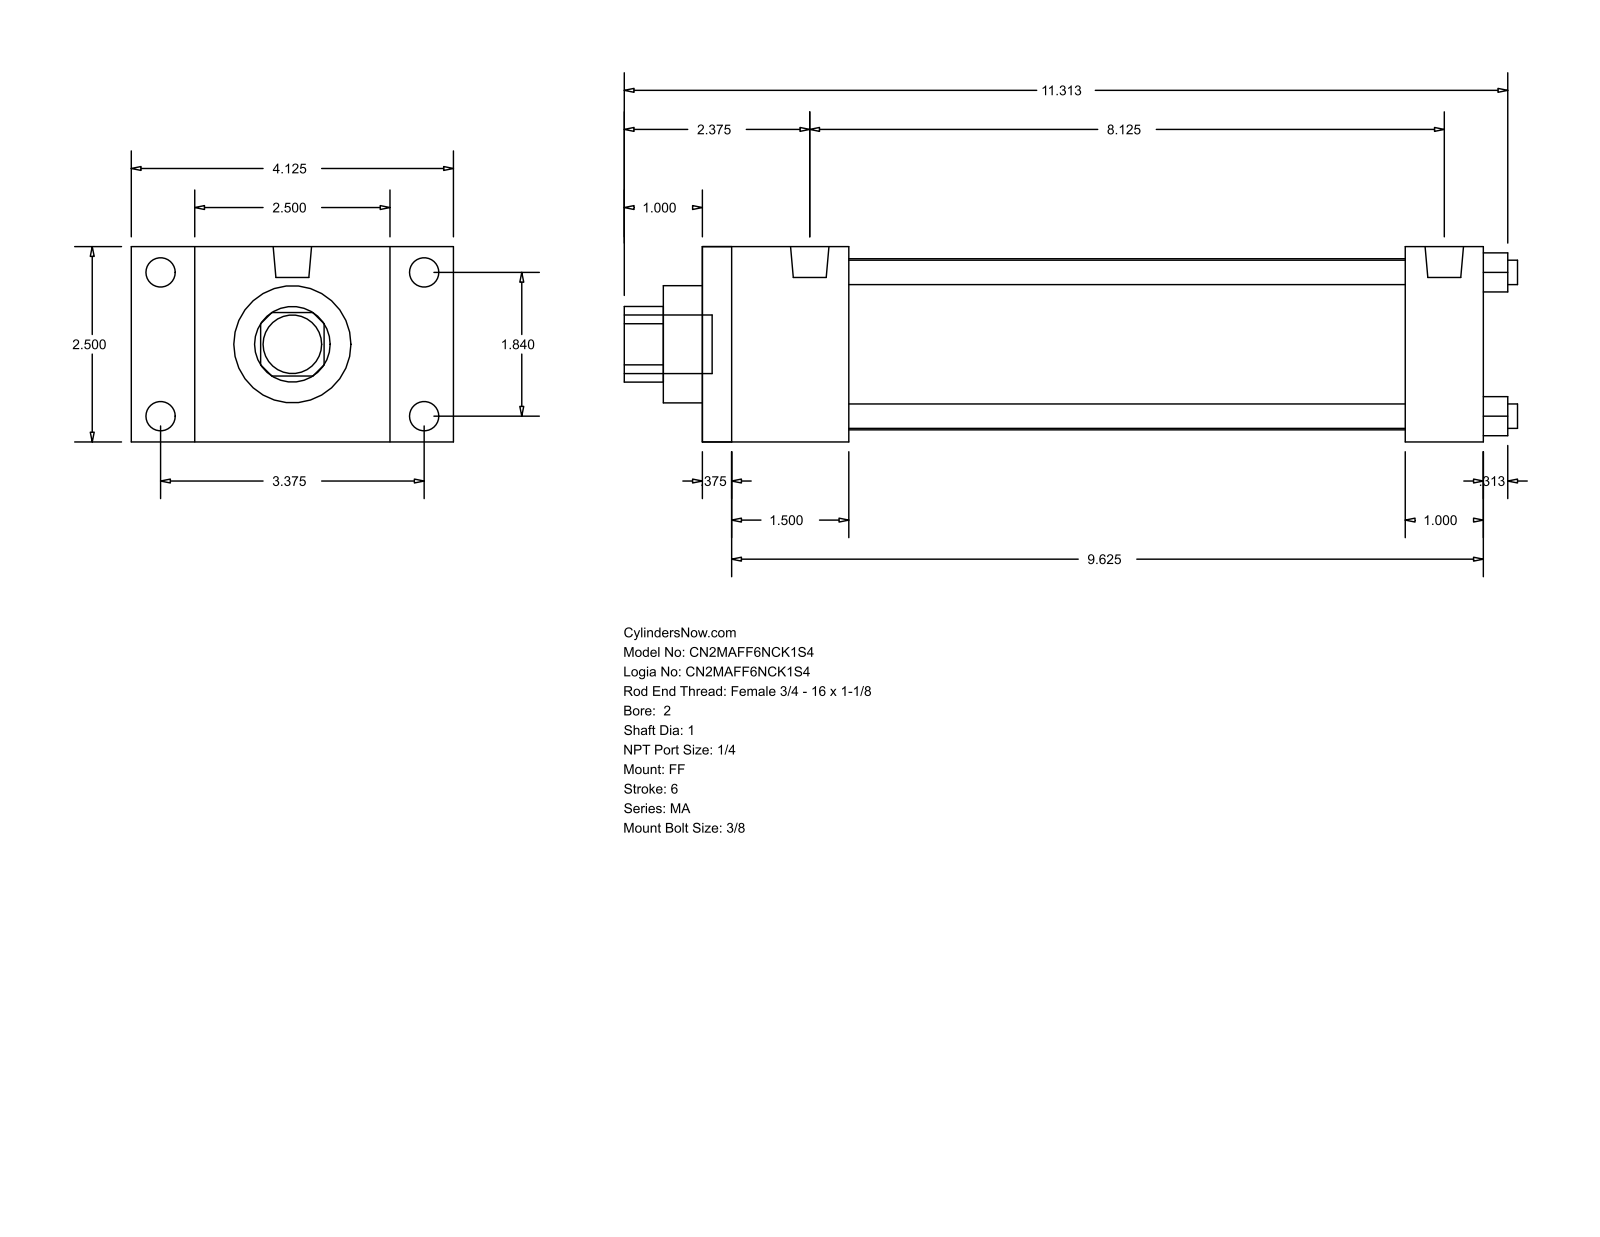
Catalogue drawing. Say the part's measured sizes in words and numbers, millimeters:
The part is named "MA_FF__0200_1". Its 3-D file was written by "GSSL Pune (CONFIG_CONTROL_DESIGN)". It is 0 solids with 92 faces: 64 planar, 28 cylindrical and 0 other. Overall it measures 290.51 by 104.78 by 63.5 millimeters. Round holes: 4 of diameter 7.94, 1 of diameter 25.4, 1 of diameter 38.1, 1 of diameter 55.63. Round bosses or shafts: 4 of diameter 9.53, 4 of diameter 7.94, 2 of diameter 12.49, 1 of diameter 19.05. Partial cylindrical surfaces (rounded edges, fillets, slot ends): 1 of radius 12.29. The main face-to-face distances are 63.5, 254, 9.52, 244.48, 25.4, 20.64, 12.7, 47.63, 228.6, 38.11. The hole center spacings are 33.05, 46.74, 66.1.
